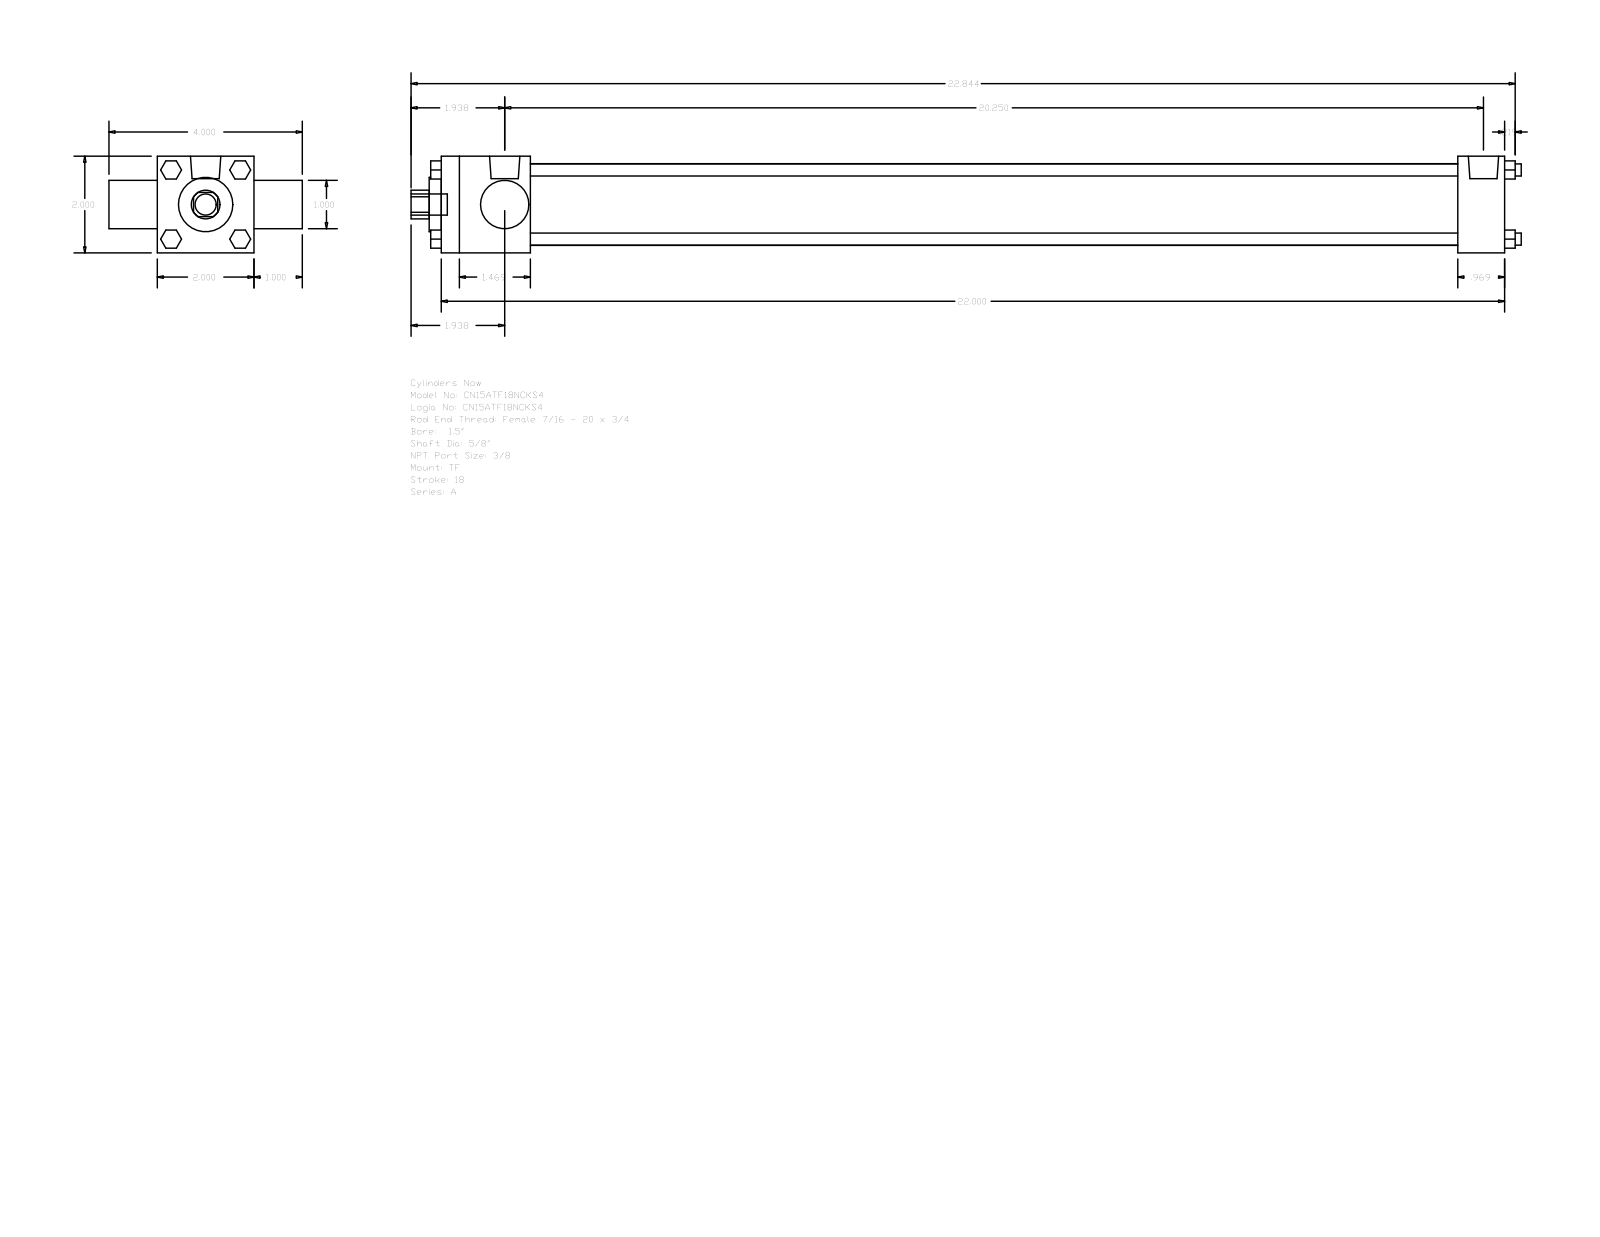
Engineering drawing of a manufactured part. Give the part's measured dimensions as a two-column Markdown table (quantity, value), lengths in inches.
| quantity | value |
| --- | --- |
| part name | A_TF__0150_0.625 |
| STEP written by | GSSL Pune (CONFIG_CONTROL_DESIGN) |
| units | inches |
| bodies | 0 solids, 120 faces (92 planar, 28 cylindrical, 0 other) |
| overall size | 22.969 × 4 × 2 |
| round holes (diameter × count) | 0.625 × 1, 1 × 1, 1.125 × 1, 1.69 × 1 |
| round bosses / shafts (diameter × count) | 0.25 × 4, 0.219 × 3, 0.627 × 2, 0.437 × 1 |
| partial cylindrical surfaces (radius × count) | 0.297 × 1 |
| main face-to-face distances | 2, 22, 1, 3, 1.844, 21.031, 19.187, 20.156, 0.969, 0.375 |
